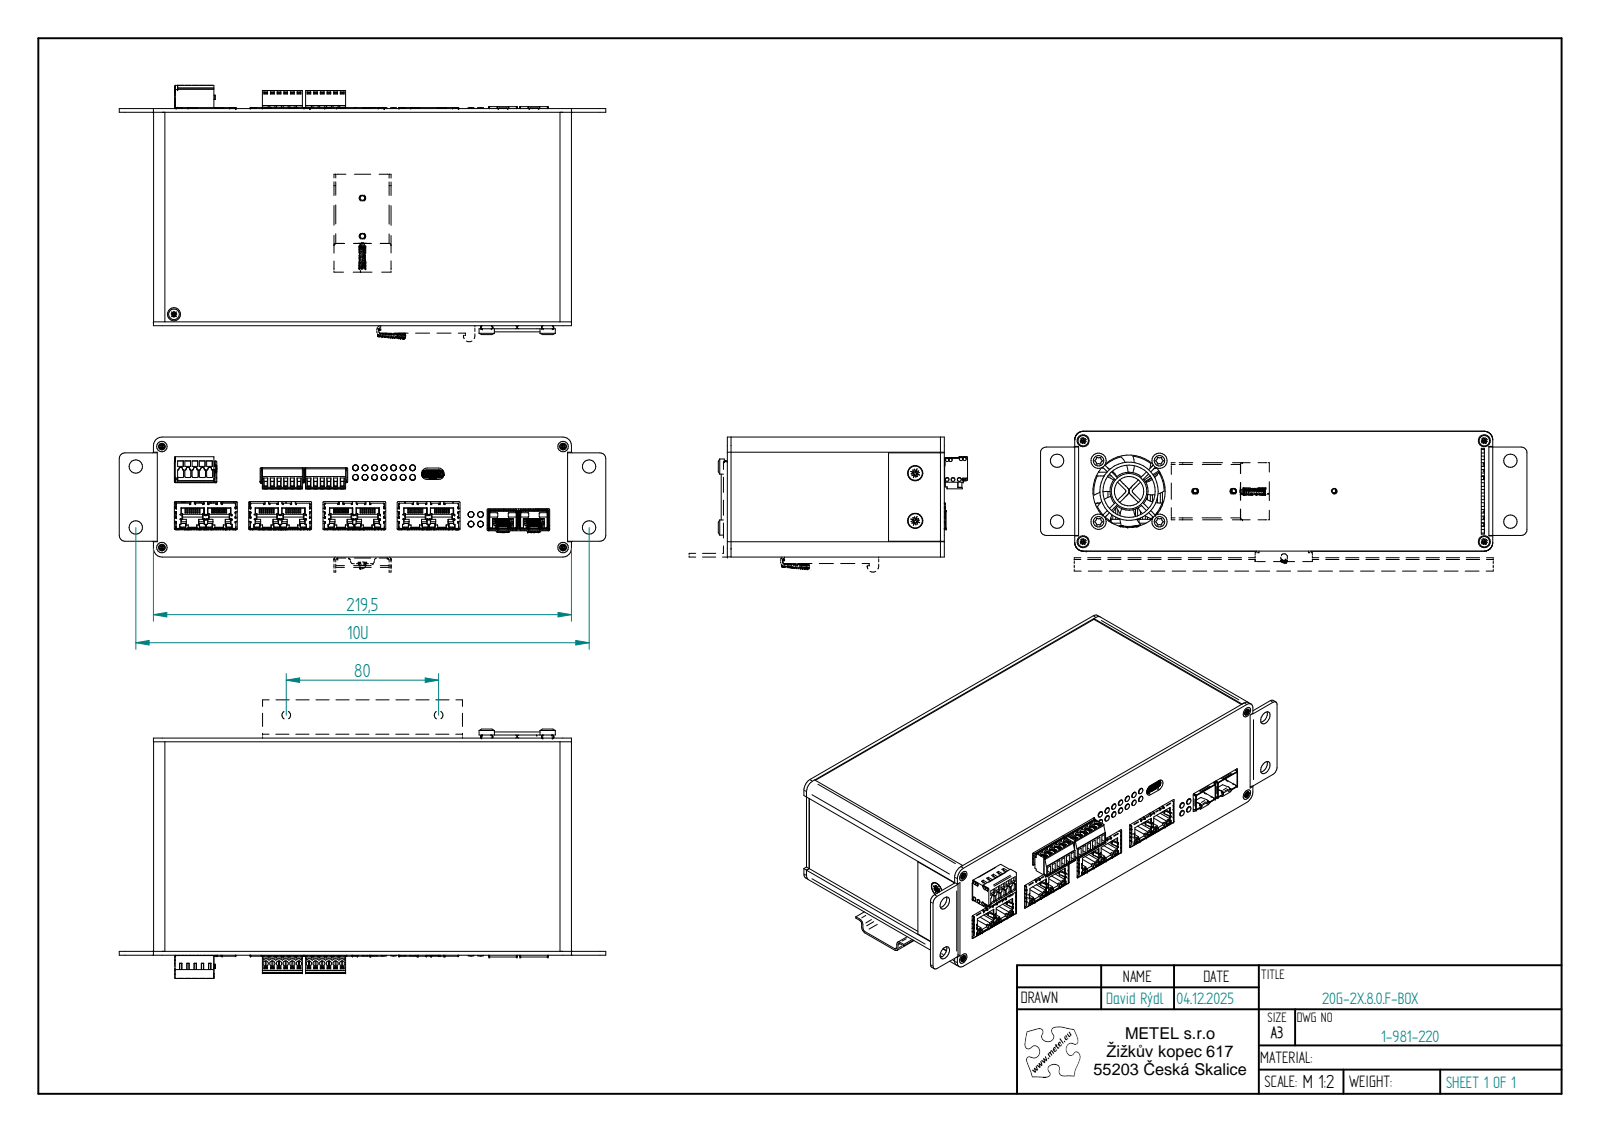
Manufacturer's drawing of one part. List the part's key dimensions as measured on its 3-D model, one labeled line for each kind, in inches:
Part name (STEP PRODUCT): 20G-2X.8.0.F; Profil 210-2X.8.0-zak; 1-981-220-20250520-005-20G-2X.8.0.F-Predni - kopie; 734-205 (+8 more)
STEP written by: Solid Edge (AUTOMOTIVE_DESIGN)
Units: inches
Bodies: 121 solids, 15804 faces (11095 planar, 3823 cylindrical, 886 other)
Overall size (bounding box): 10.059 × 5.152 × 2.89
Volume: 18.64 in³ · Surface area: 473.1 in²
Round holes (diameter × count): ⌀0.13 ×19, ⌀0.059 ×17, ⌀0.075 ×12, ⌀0.083 ×12, ⌀0.11 ×12, ⌀0.138 ×6, ⌀0.097 ×5, ⌀0.018 ×4, ⌀0.106 ×4, ⌀0.136 ×4, ⌀0.169 ×4, ⌀0.197 ×4
Round bosses / shafts (diameter × count): ⌀0.118 ×19, ⌀0.059 ×18, ⌀0.071 ×14, ⌀0.157 ×6, ⌀0.315 ×4, ⌀0.217 ×4, ⌀0.181 ×4, ⌀0.114 ×4
Partial cylindrical surfaces — rounded edges, fillets, slot ends (radius × count): R0.004 ×402, R0.01 ×224, R0.008 ×182, R0.012 ×163, R0.006 ×132, R0.02 ×82, R0.039 ×65, R0.035 ×32
Main face-to-face distances: 0.113, 2.328, 0.079, 4.409, 2.441, 2.214, 4.331, 0.157, 8.327, 4.488
Hole centre spacings: 0.197, 0.28, 0.138, 0.394, 0.441, 0.199, 0.276, 0.591
